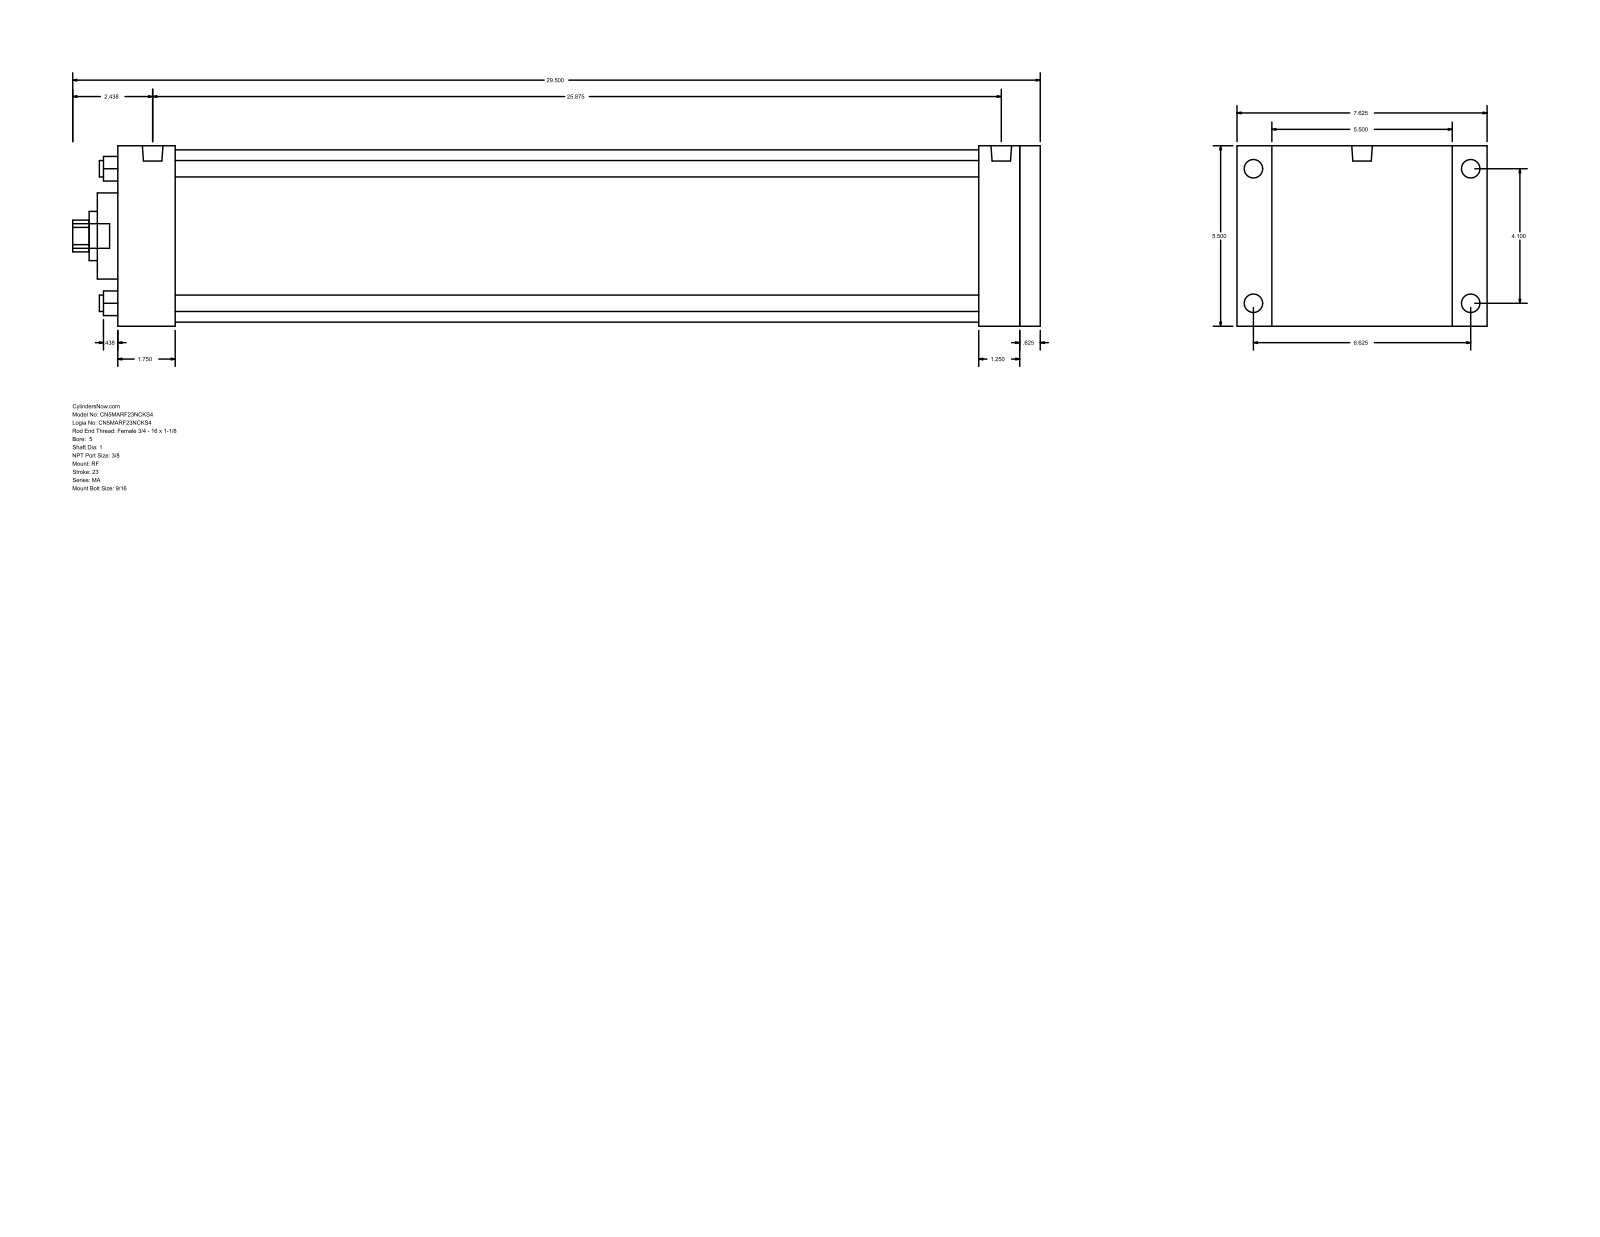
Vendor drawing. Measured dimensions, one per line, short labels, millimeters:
name: MA_RF__0500_1
written by: GSSL Pune (CONFIG_CONTROL_DESIGN)
unit: mm
bodies: 0 solids, 94 faces (65 planar, 29 cylindrical, 0 other)
size: 749.3 × 193.68 × 139.7
holes: 4× ⌀12.7, 1× ⌀25.4, 1× ⌀38.1, 1× ⌀66.67, 1× ⌀133.35
bosses: 4× ⌀14.29, 4× ⌀11.11, 2× ⌀15.93, 1× ⌀19.05
rounds: 1× R12.29
face distances: 139.7, 714.38, 698.5, 15.88, 44.46, 654.04, 669.92, 666.75, 622.29, 31.75
hole spacings: 73.64, 104.14, 147.28
